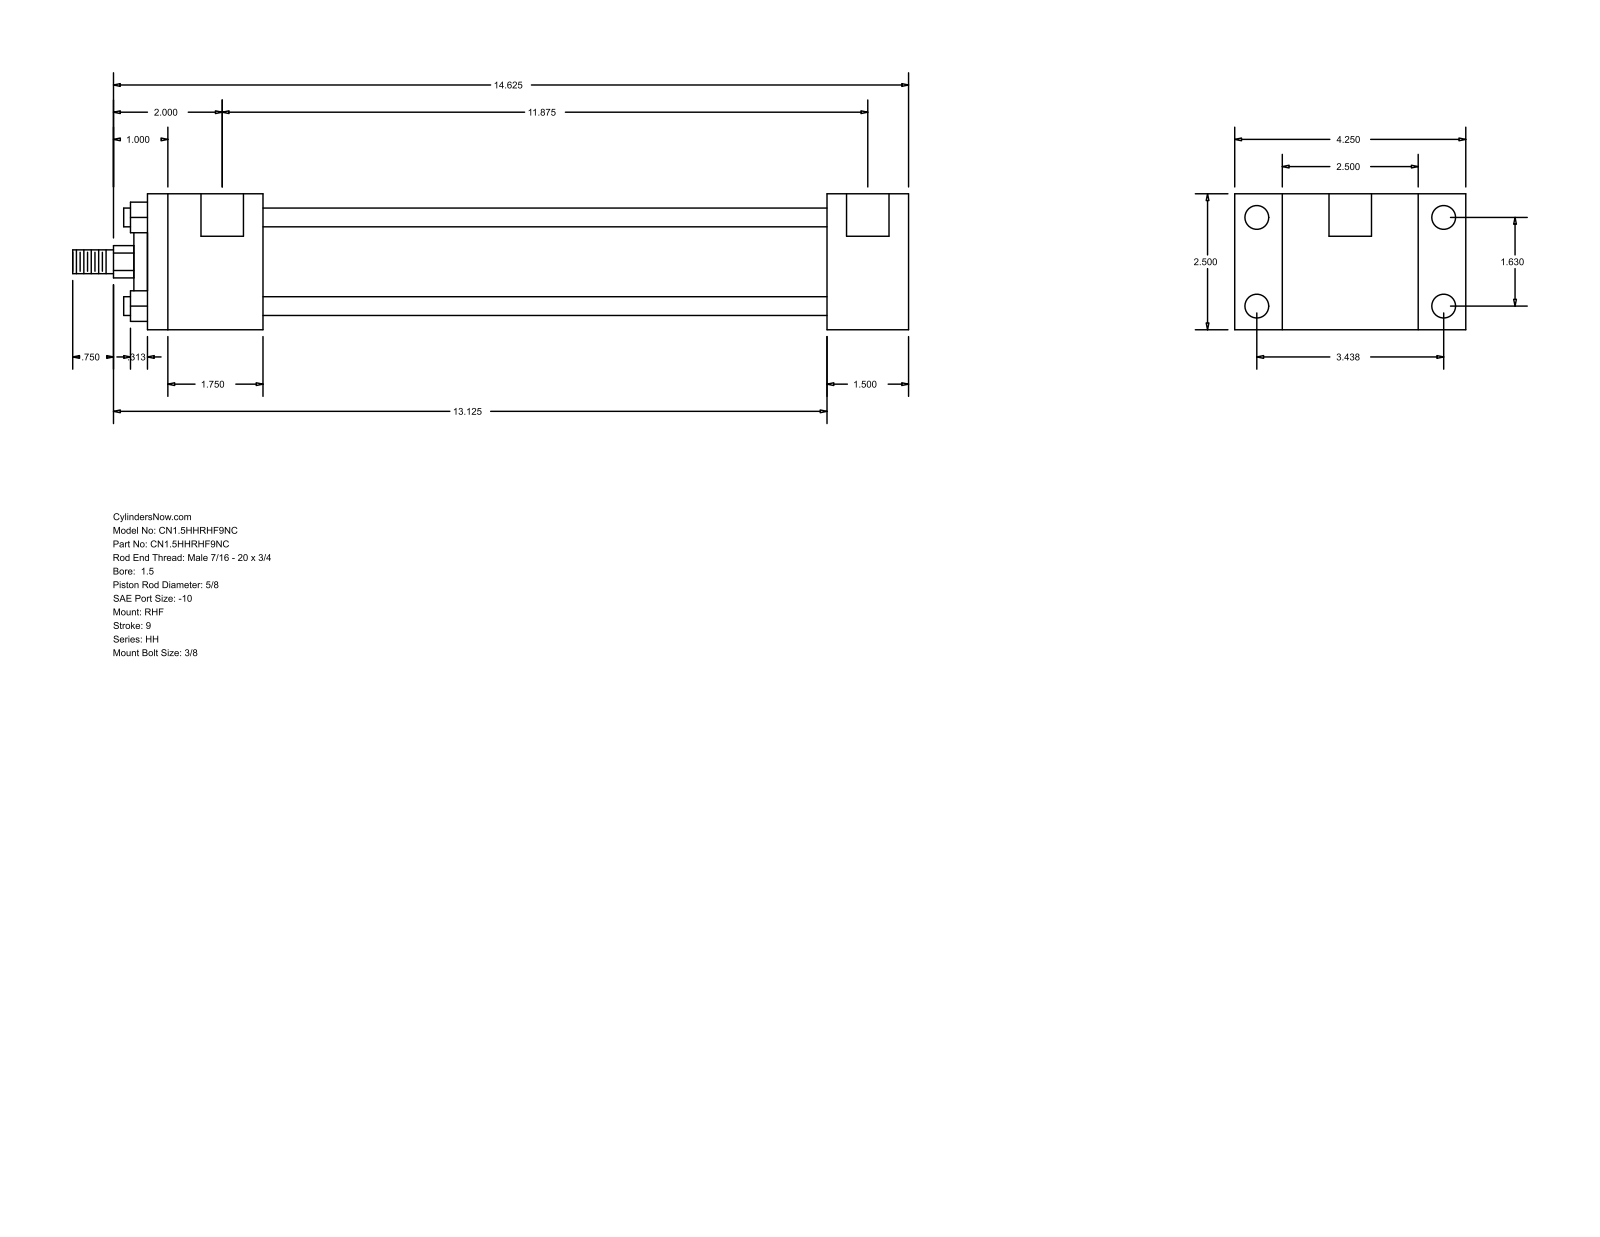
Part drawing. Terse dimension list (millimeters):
name: HH_RHF__0150_0.625
written by: GSSL Pune (CONFIG_CONTROL_DESIGN)
unit: mm
bodies: 0 solids, 88 faces (60 planar, 28 cylindrical, 0 other)
size: 390.52 × 107.95 × 63.5
holes: 4× ⌀5.56, 4× ⌀11.13, 2× ⌀19.84
bosses: 4× ⌀8.76, 1× ⌀44.45, 1× ⌀28.57, 1× ⌀15.88, 1× ⌀11.11
rounds: 1× R7.54
face distances: 63.5, 38.1, 22.23, 85.73, 317.5, 355.6, 107.96, 53.97, 263.53, 301.63
hole spacings: 41.4, 87.32, 96.64, 304.8, 1.58, 1.59, 301.63, 303.21
